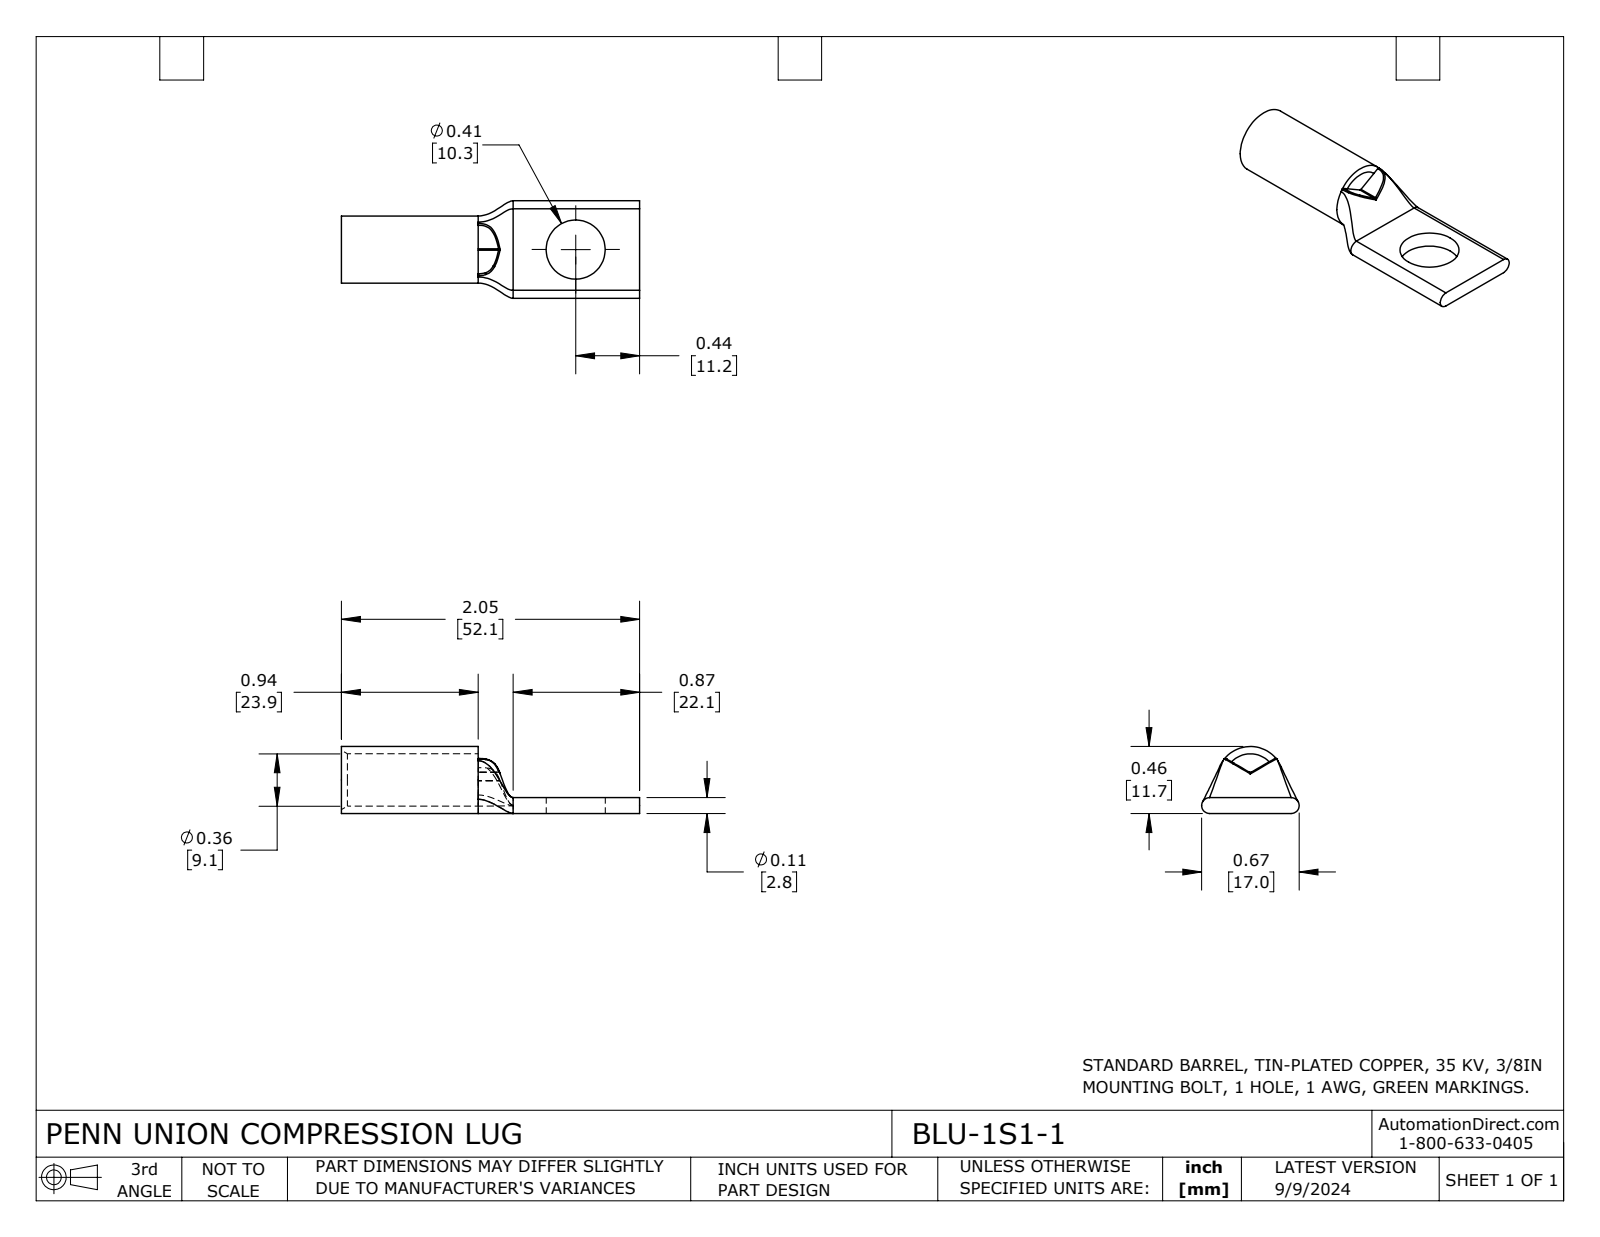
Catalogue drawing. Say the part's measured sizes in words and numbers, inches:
The part is named "BLU-1S1-1". Its 3-D file was written by "SolidWorks 2023 (CONFIG_CONTROL_DESIGN)". It is 1 solid with 39 faces: 11 planar, 11 cylindrical and 17 other. Overall it measures 2.05 by 0.67 by 0.461 inches. Its volume is 0.124 cubic inches and its surface area 4.499 square inches. Round holes: 1 of diameter 0.36, 1 of diameter 0.406. Round bosses or shafts: 1 of diameter 0.461. Partial cylindrical surfaces (rounded edges, fillets, slot ends): 2 of radius 0.01, 2 of radius 0.055. The main face-to-face distances are 0.11, 0.05, 2.05, 0.94, 1.11, 1.18, 0.24, 0.87.
